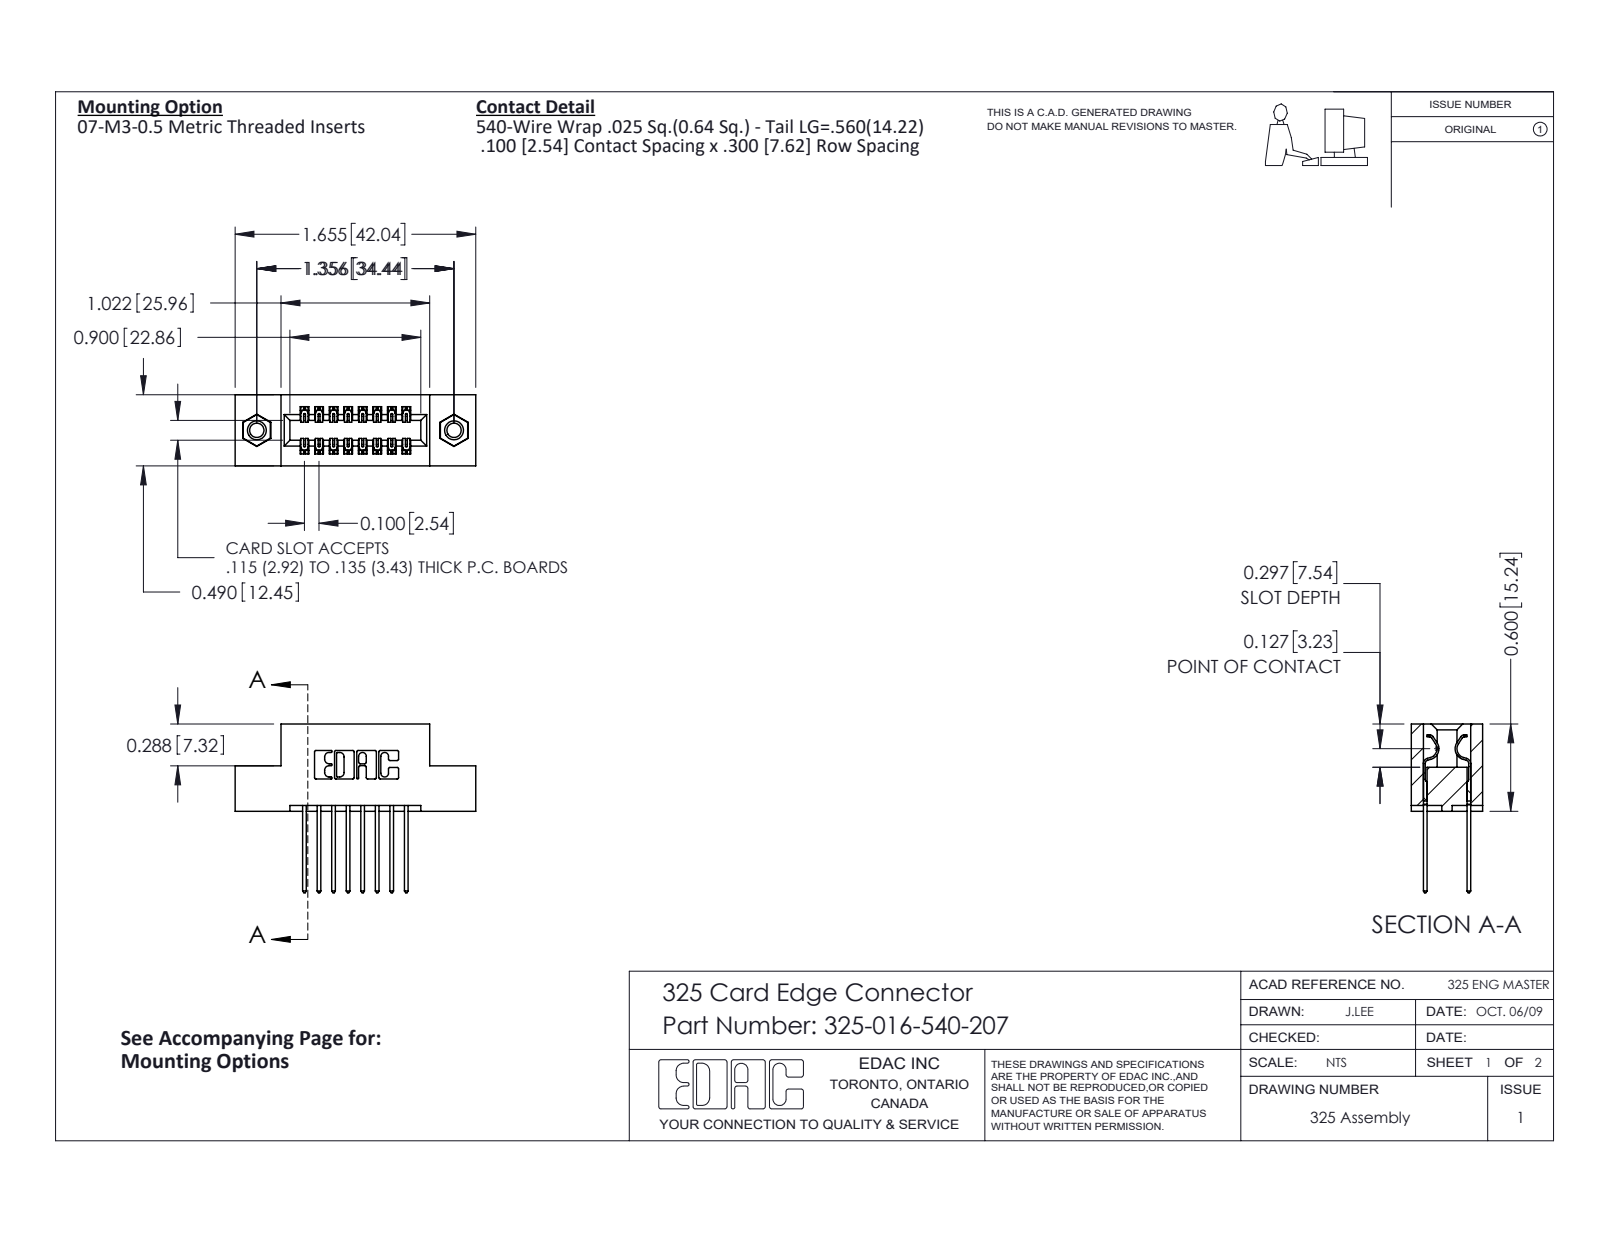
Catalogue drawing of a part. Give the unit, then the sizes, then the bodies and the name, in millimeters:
Units: millimetres
Overall size (bounding box): 42 × 29.5 × 12.4
Round holes (diameter × count): ⌀2.5 ×2, ⌀3.2 ×2, ⌀4.1 ×2
Round bosses / shafts (diameter × count): ⌀3.9 ×2
Partial cylindrical surfaces — rounded edges, fillets, slot ends (radius × count): R0.2 ×24, R0.3 ×22, R0.3 ×16, R0.2 ×6, R0.8 ×6, R0.7 ×3, R0.4 ×2, R0.6 ×2
Main face-to-face distances: 7.6, 2.1, 10.3, 2.5, 5.1, 1, 12.4, 2.7, 9.7, 0.6
Hole centre spacings: 34.4
Volume: 5 160 mm³ · Surface area: 5 765 mm²
Bodies: 19 solids, 1006 faces (678 planar, 312 cylindrical, 16 other)
Part name (STEP PRODUCT): 325-292-001_325-293-140; 345-250-001_345-250-005-103; 325-016-540-207; 325 Part_TI
STEP written by: SolidWorks 2016 (CONFIG_CONTROL_DESIGN)
